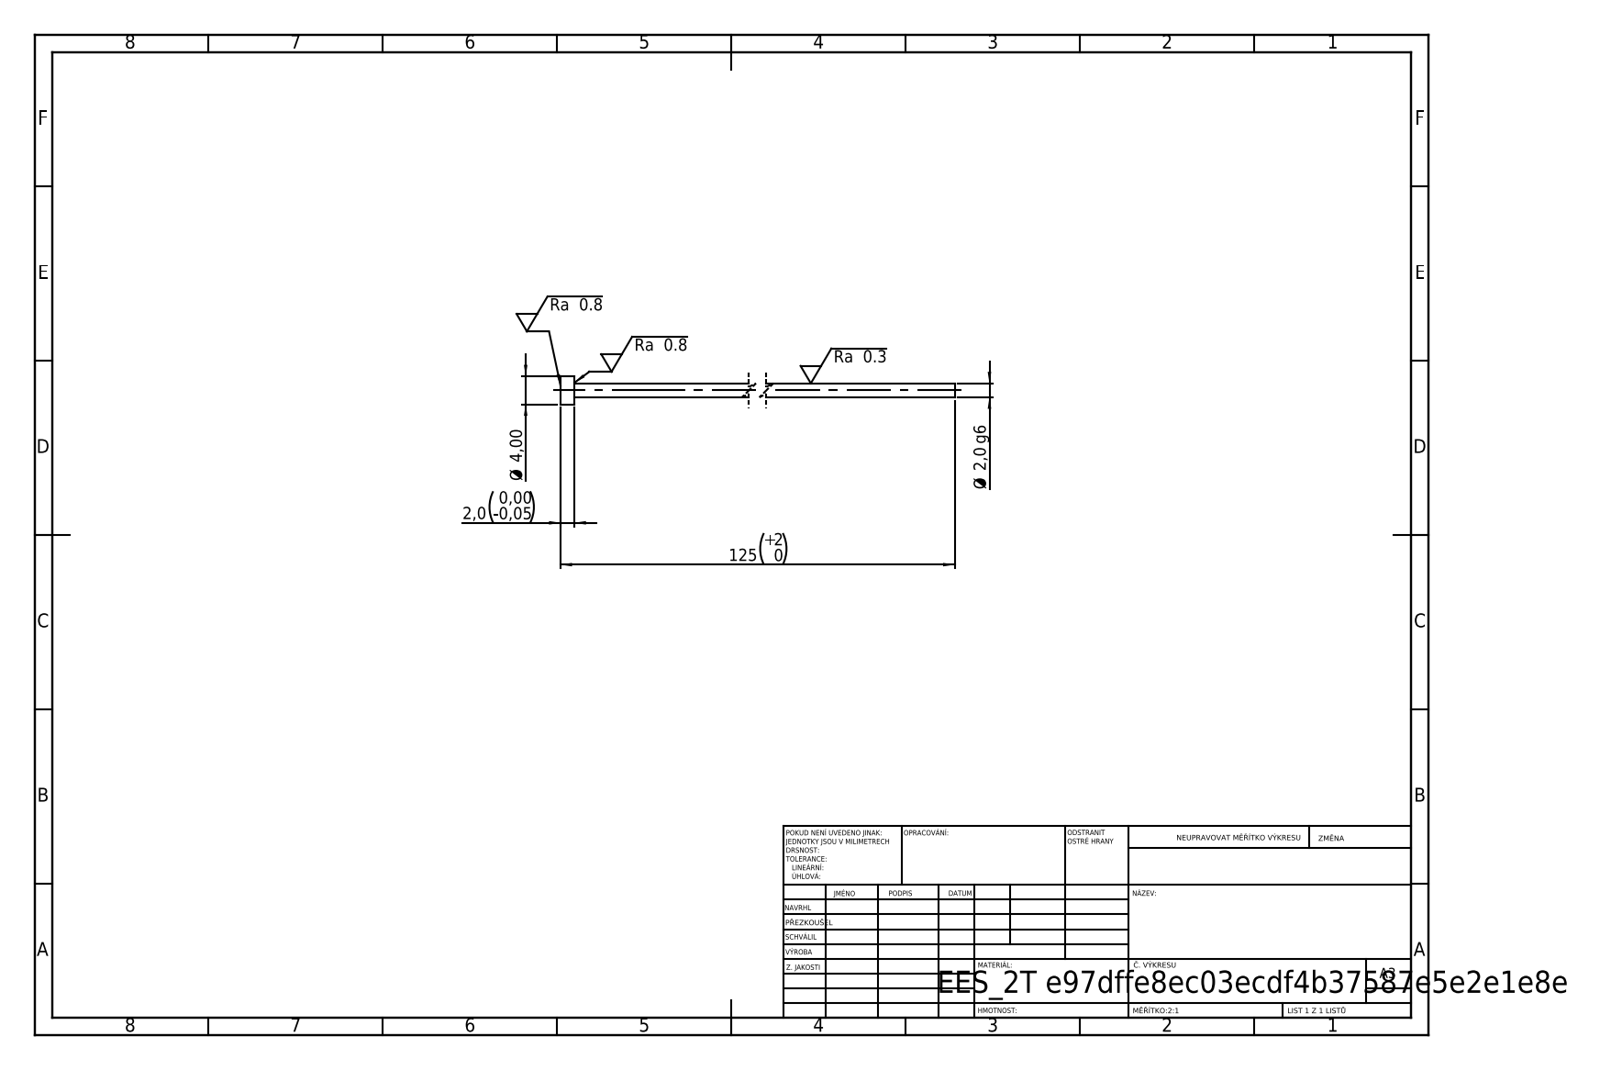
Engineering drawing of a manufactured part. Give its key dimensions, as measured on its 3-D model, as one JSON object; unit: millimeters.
{"step_written_by": "SolidWorks 2019 (CONFIG_CONTROL_DESIGN)", "units": "millimeters", "bodies": {"solids": 1, "faces": 7, "planar": 3, "cylindrical": 4, "other": 0}, "overall_size": [125, 4, 4], "volume_mm3": 412, "surface_area_mm2": 823, "round_bosses_or_shafts": [[4, 1], [2, 1]], "face_to_face_distances": [2, 125, 123]}
